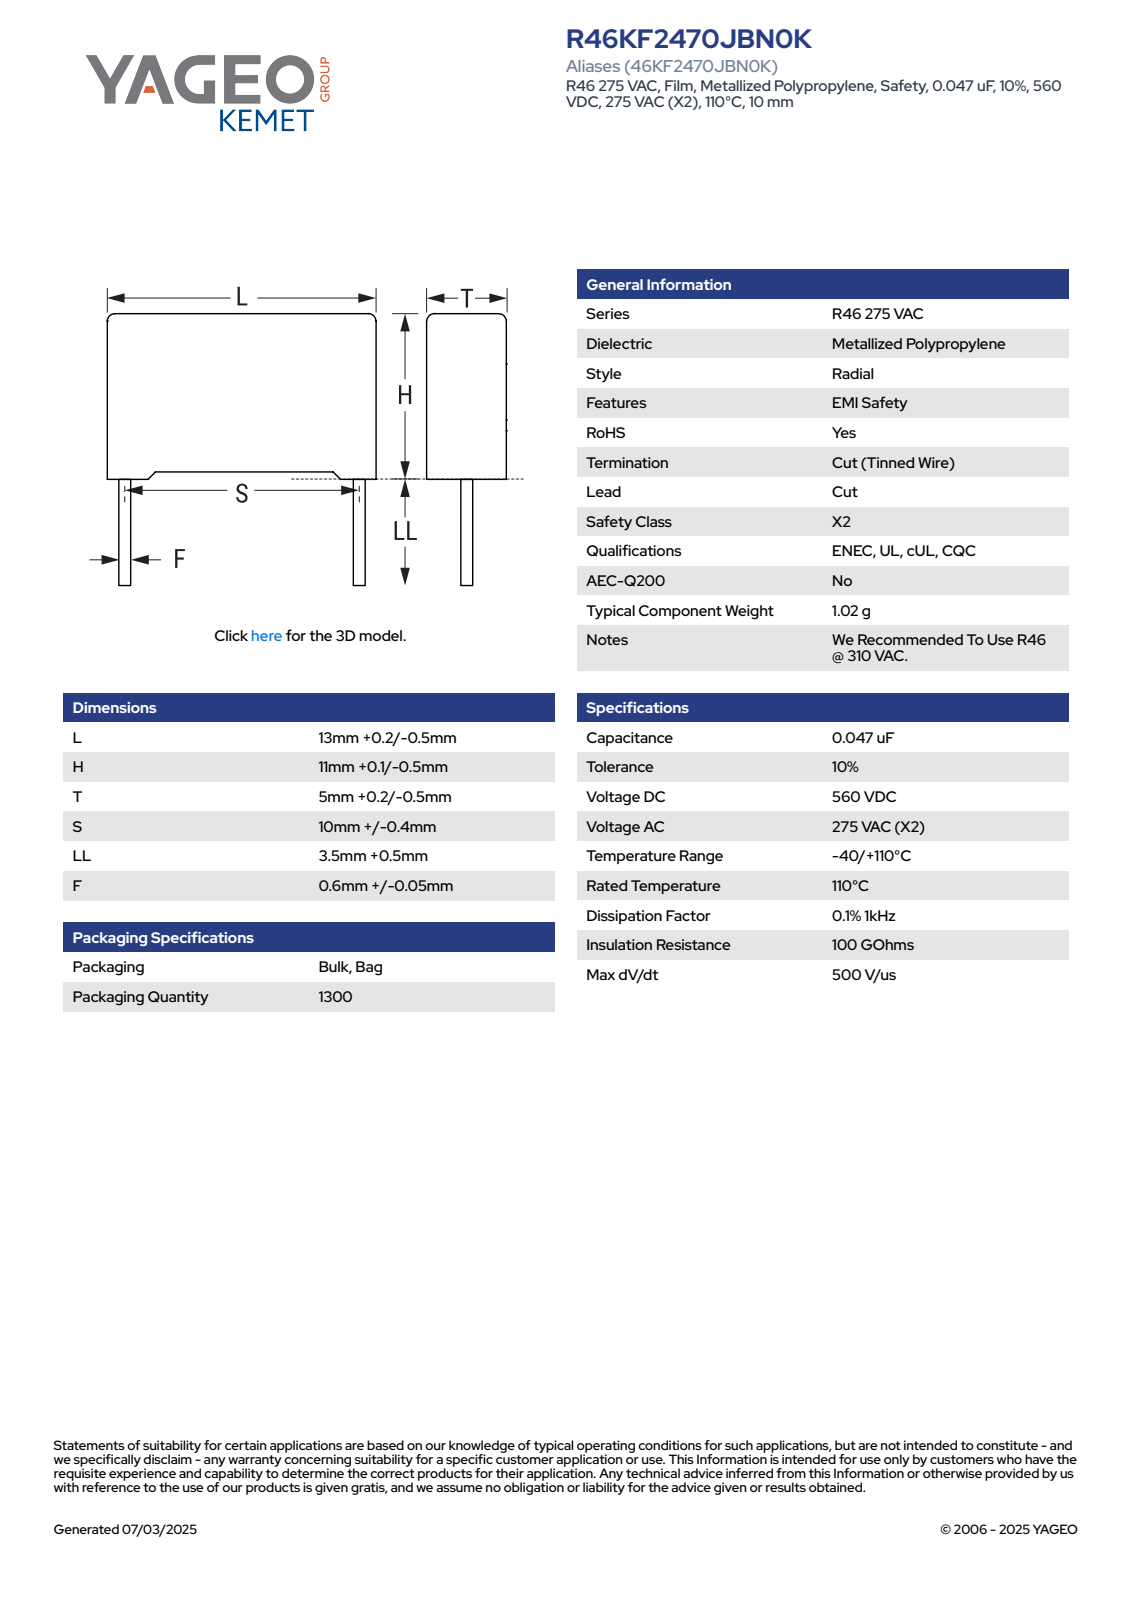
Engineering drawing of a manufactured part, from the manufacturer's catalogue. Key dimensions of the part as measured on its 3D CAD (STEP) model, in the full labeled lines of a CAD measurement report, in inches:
Part name (STEP PRODUCT): CFR_RB2_13X11X5_L13.2H11.1T5.2S10LL4F0.65
STEP written by: SolidWorks 2021 (AUTOMOTIVE_DESIGN)
Units: inches
Bodies: 4 solids, 85 faces (77 planar, 8 cylindrical, 0 other)
Overall size (bounding box): 0.594 × 0.52 × 0.205
Volume: 0.044 in³ · Surface area: 0.907 in²
Round bosses / shafts (diameter × count): ⌀0.026 ×2
Partial cylindrical surfaces — rounded edges, fillets, slot ends (radius × count): R0.02 ×4
Main face-to-face distances: 0.205, 0.52, 0.407, 0.017, 0.187, 0.03, 0.437, 0.17, 0.502, 0.015
